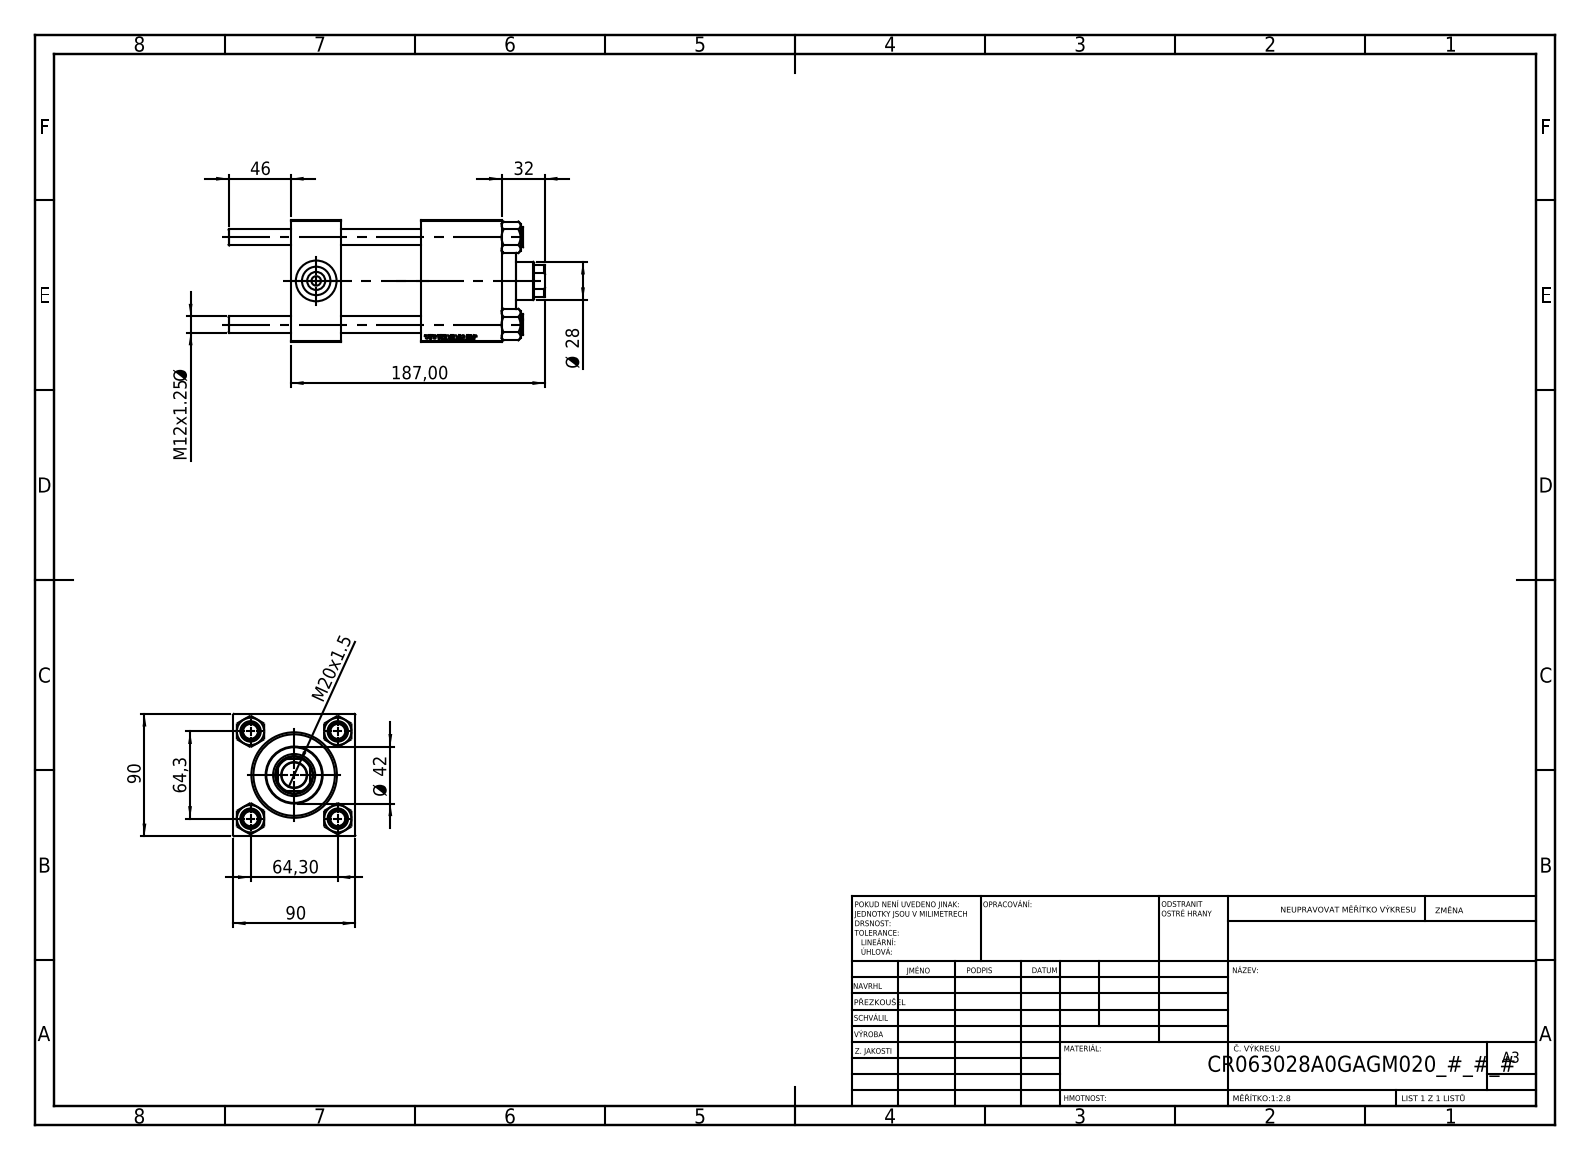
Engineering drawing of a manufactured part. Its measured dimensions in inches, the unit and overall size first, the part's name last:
Units: inches
Overall size (bounding box): 9.173 × 3.543 × 3.543
Round holes (diameter × count): ⌀0.472 ×4, ⌀0.276 ×2, ⌀0.825 ×2, ⌀1.181 ×2, ⌀0.728 ×1, ⌀1.102 ×1, ⌀1.22 ×1, ⌀1.969 ×1, ⌀2.362 ×1, ⌀2.48 ×1
Round bosses / shafts (diameter × count): ⌀0.591 ×4, ⌀2.717 ×1, ⌀1.654 ×1
Partial cylindrical surfaces — rounded edges, fillets, slot ends (radius × count): R0.531 ×1
Main face-to-face distances: 3.543, 2.323, 1.457, 6.102, 4.646, 3.78, 4.972, 3.516, 1.193, 1.13
Hole centre spacings: 1.79, 2.531, 3.58
Volume: 59.82 in³ · Surface area: 303.3 in²
Bodies: 11 solids, 1134 faces (519 planar, 79 cylindrical, 536 other)
Part name (STEP PRODUCT): V215CR_VCP; NUT_M5; CR025_012_A_0_G_A_G_M_020_+#_##_TYCINKA; V215CR_BODY_A (+1 more)
STEP written by: SolidWorks 2019 (CONFIG_CONTROL_DESIGN)
